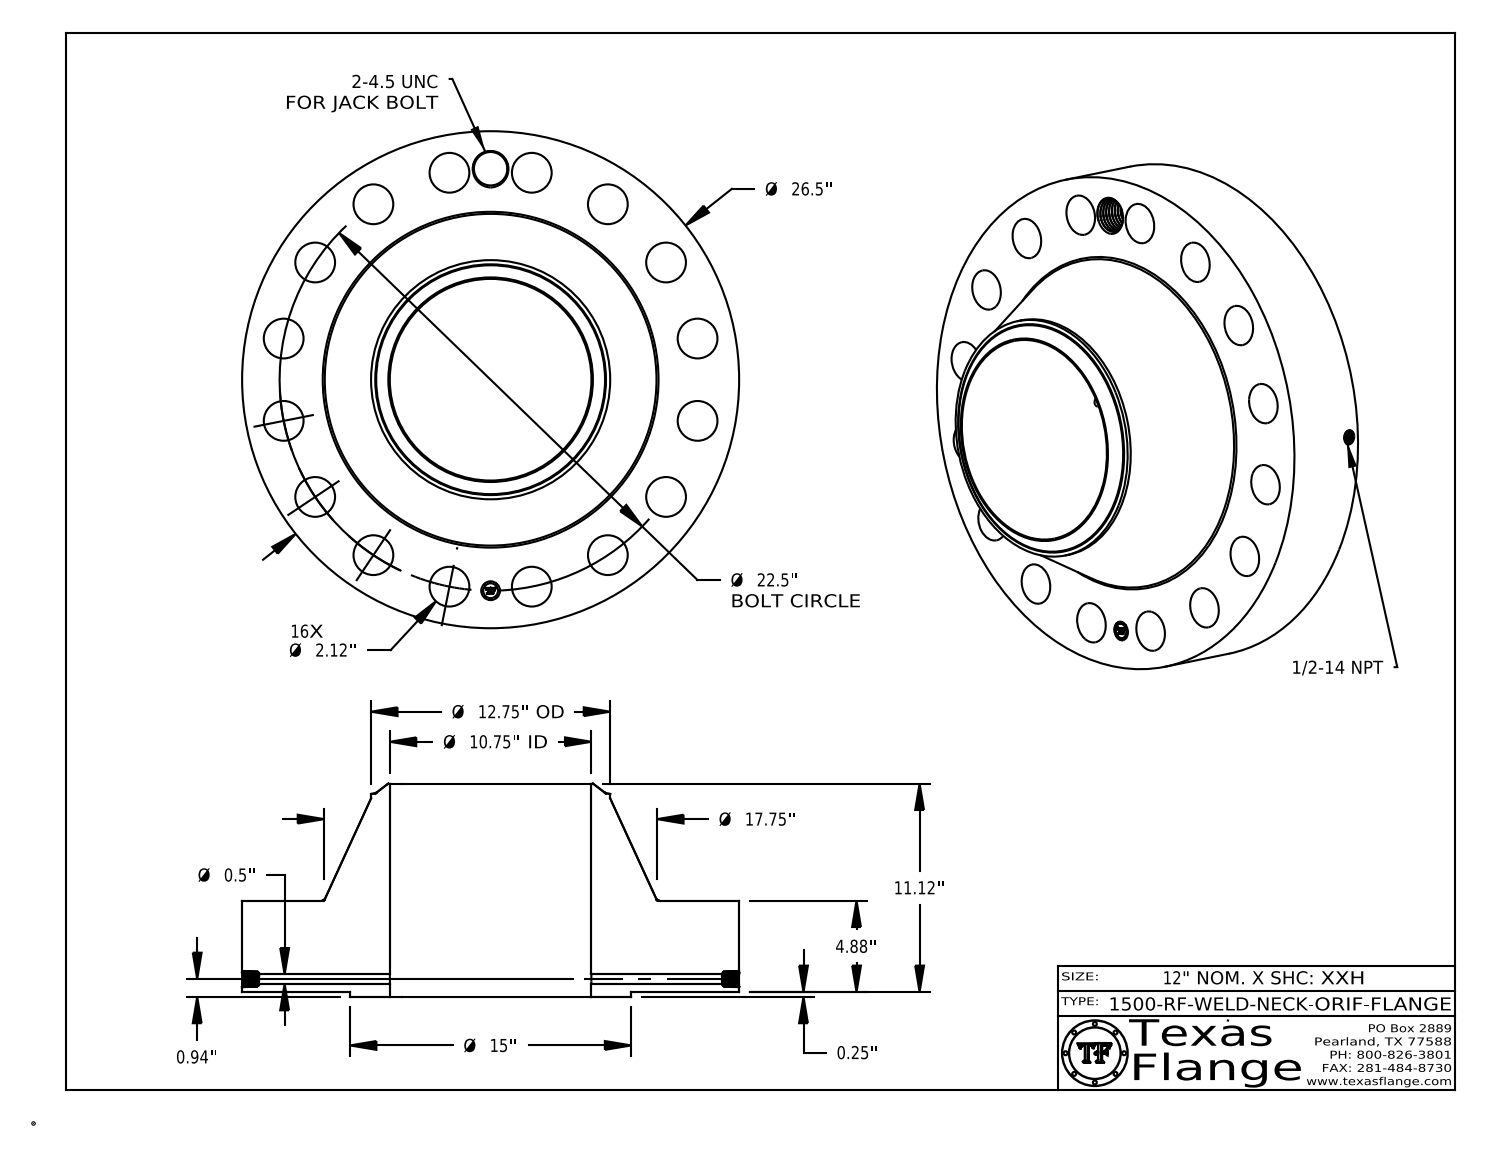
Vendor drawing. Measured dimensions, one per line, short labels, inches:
name: 1500-RF-WELD-NECK
written by: CATIA V5 STEP AP214 (AUTOMOTIVE_DESIGN)
unit: in
bodies: 1 solid, 831 faces (369 planar, 124 cylindrical, 338 other)
size: 26.5 × 26.5 × 11.37
volume: 2 504 in³; area: 2 376 in²
holes: 16× ⌀2.12, 1× ⌀0.5, 1× ⌀0.672, 1× ⌀1, 1× ⌀1.781, 1× ⌀10.75
bosses: 8× ⌀0.061, 1× ⌀26.5, 1× ⌀15, 1× ⌀12.75, 1× ⌀0.788
face distances: 4.88, 0.25, 5.13, 11.37, 11.12, 6.24, 5.115, 4.865, 0.015, 6.255
hole spacings: 11.25, 8.61, 15.91, 20.787, 12.5, 18.708, 22.068, 4.389
